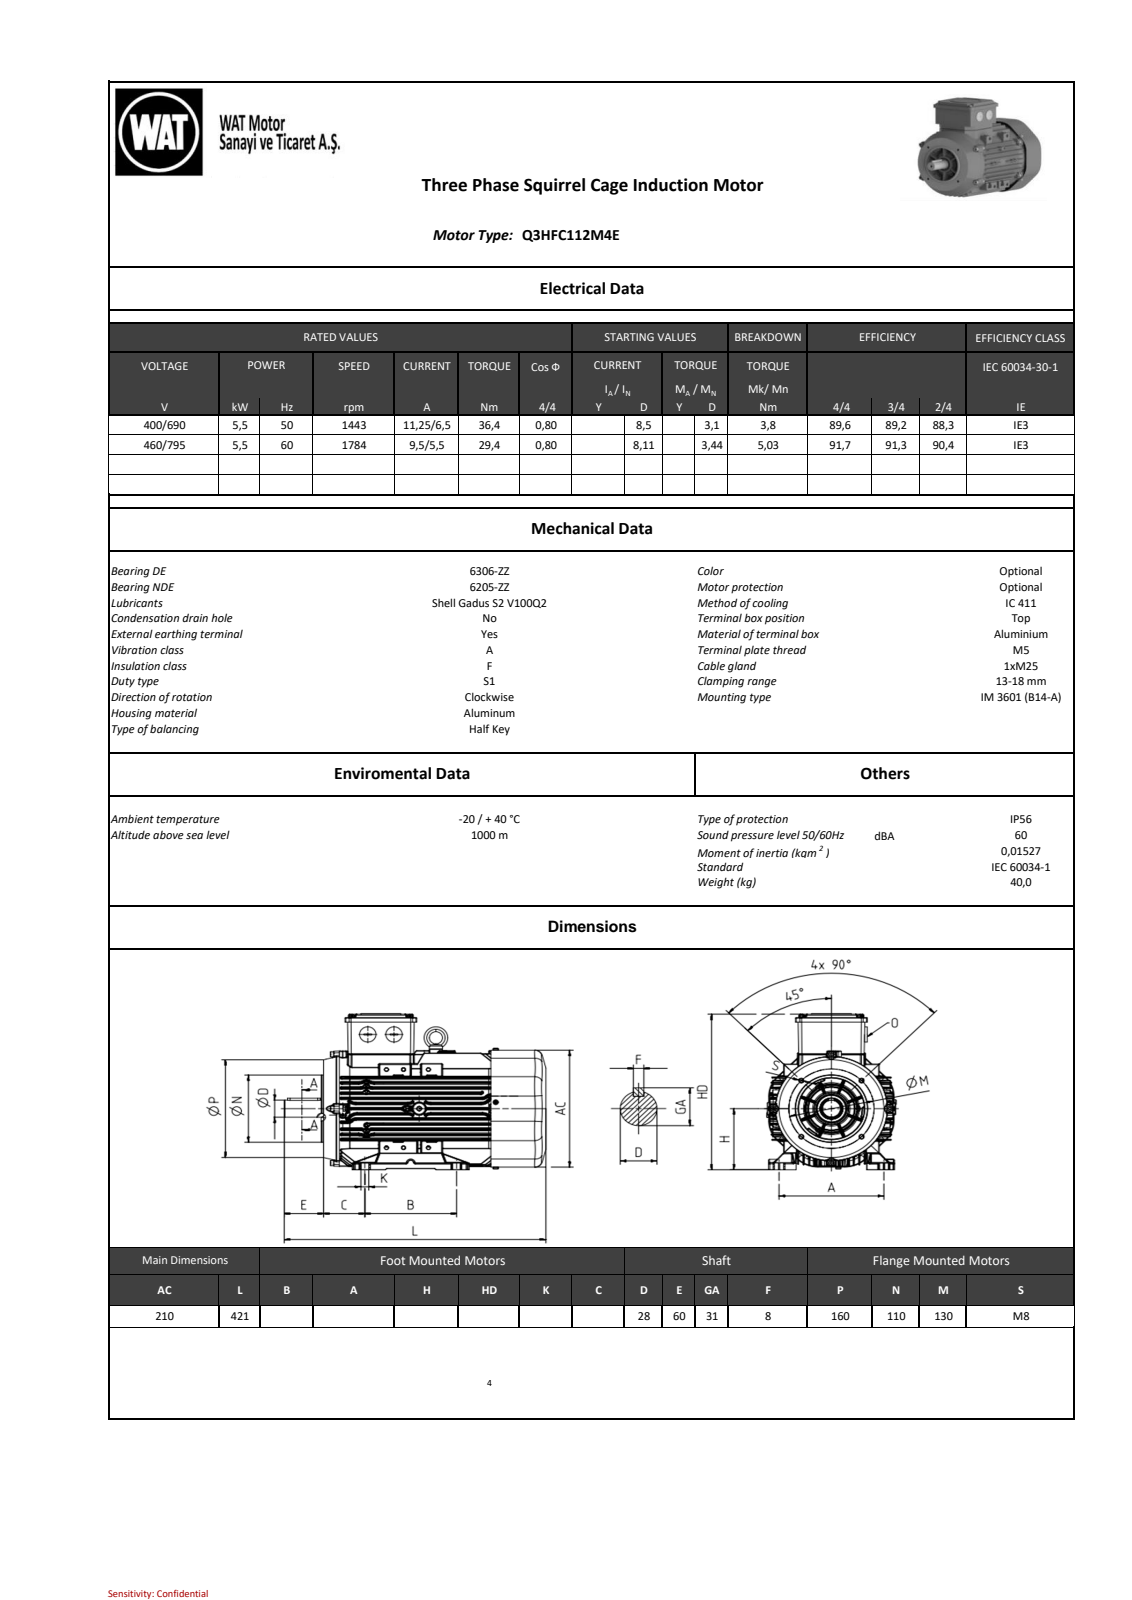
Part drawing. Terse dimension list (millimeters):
name: QH series_ 112_B14a _DEEP COVER__stp_objects
written by: SIEMENS PLM Software NX2206.8101 (AUTOMOTIVE_DESIGN)
unit: mm
bodies: 0 solids, 6664 faces (1493 planar, 2556 cylindrical, 2615 other)
size: 421 × 267.5 × 219
holes: 2× ⌀3.5, 2× ⌀4.6, 1× ⌀8, 1× ⌀8.5, 1× ⌀47, 1× ⌀78
bosses: 6× ⌀8, 4× ⌀10, 2× ⌀25, 2× ⌀6, 1× ⌀188, 1× ⌀110, 1× ⌀35.83, 1× ⌀30
rounds: 615× R2, 525× R0.8, 352× R0.5, 272× R1, 95× R1.2, 65× R3, 10× R4, 4× R2.5
face distances: 1, 10.99, 21.5, 35.96, 99.54, 90.43, 24.97, 68.93, 8.16, 112.88
